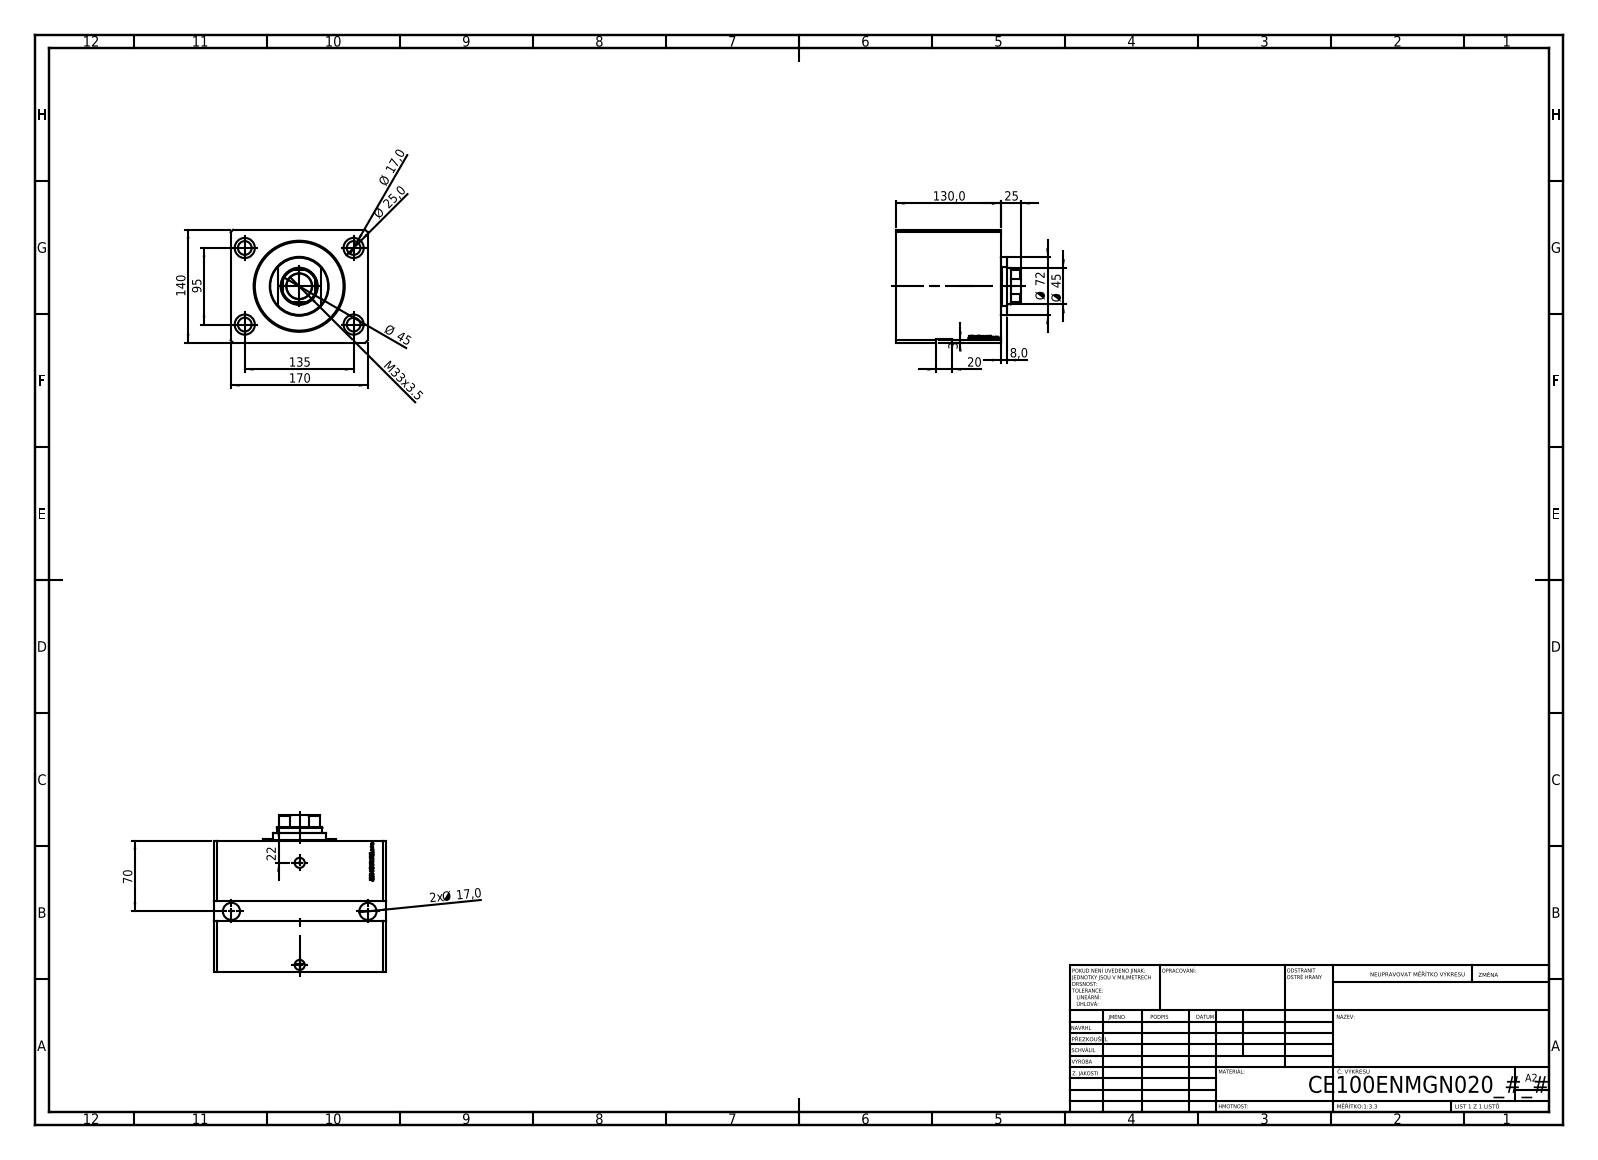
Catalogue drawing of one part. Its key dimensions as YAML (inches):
part_name: "V250CE_C_VCP; V250CE_VC_E; V250CE_E_Body"
step_written_by: "SolidWorks 2019 (CONFIG_CONTROL_DESIGN)"
units: inches
bodies: {solids: 3, faces: 933, planar: 471, cylindrical: 76, other: 386}
overall_size: [6.693, 6.102, 5.512]
volume: 168.7
surface_area: 435.3
round_holes:
  - {diameter: 0.669, count: 6}
  - {diameter: 0.049, count: 4}
  - {diameter: 0.984, count: 4}
  - {diameter: 0.394, count: 2}
  - {diameter: 0.518, count: 2}
  - {diameter: 0.787, count: 2}
  - {diameter: 1.24, count: 1}
  - {diameter: 1.772, count: 1}
  - {diameter: 3.937, count: 1}
  - {diameter: 4.449, count: 1}
round_bosses_or_shafts:
  - {diameter: 2.835, count: 1}
partial_cylinders:
  - {radius: 0.866, count: 1}
face_to_face_distances: [5.512, 5.118, 6.693, 1.138, 3.98, 0.984, 4.134, 2.996, 0.787, 3.346]
hole_center_spacings: [3.25, 5.315, 3.261, 3.366, 3.379, 3.74, 6.499, 0.021]
